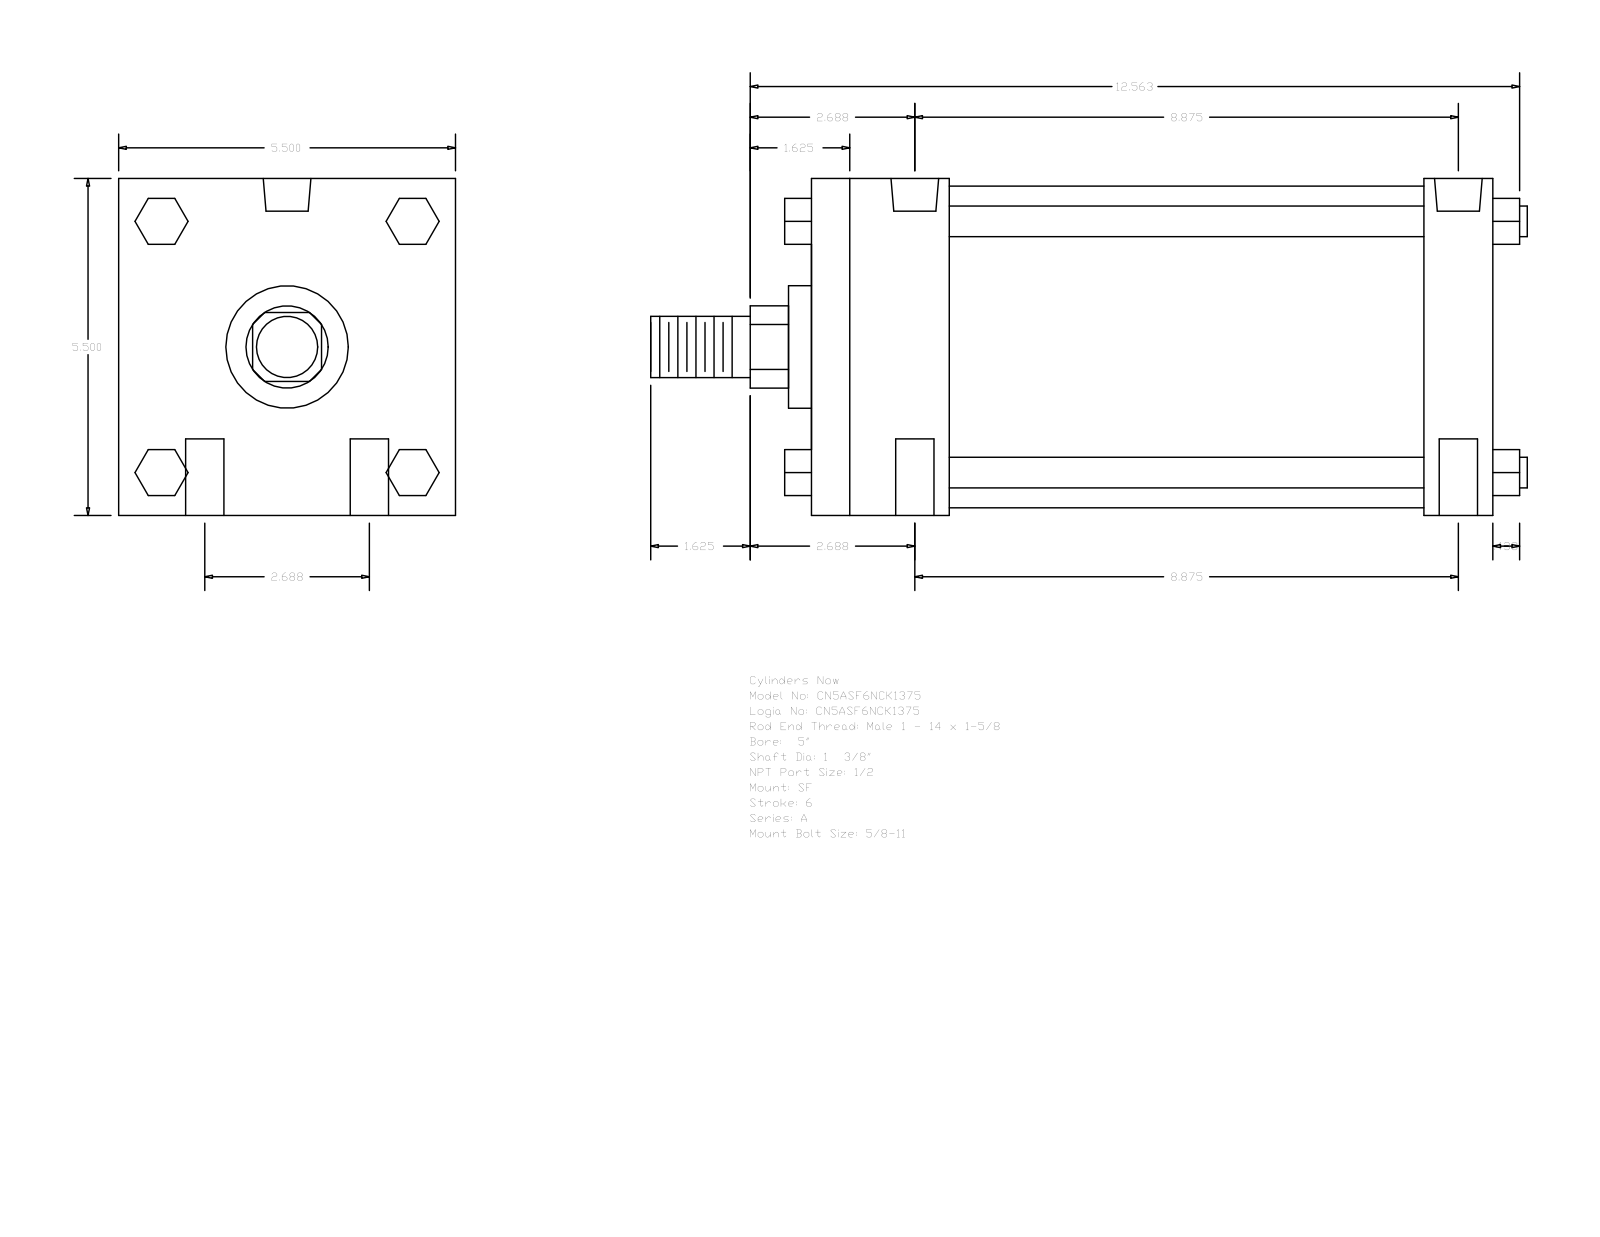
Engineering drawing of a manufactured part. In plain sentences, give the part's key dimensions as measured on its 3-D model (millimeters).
The part is named "A_SF__0500_1.375". Its 3-D file was written by "GSSL Pune (CONFIG_CONTROL_DESIGN)". It is 0 solids with 124 faces: 94 planar, 30 cylindrical and 0 other. Overall it measures 363.54 by 139.7 by 139.7 millimeters. Round holes: 4 of diameter 15.88, 2 of diameter 8.73, 2 of diameter 19.77. Round bosses or shafts: 4 of diameter 12.7, 1 of diameter 133.35, 1 of diameter 50.8, 1 of diameter 34.92, 1 of diameter 25.4. Partial cylindrical surfaces (rounded edges, fillets, slot ends): 1 of radius 17.06. The main face-to-face distances are 139.7, 282.58, 57.15, 28.58, 254, 196.85, 225.43, 19.05, 52.07, 90.18. The hole center spacings are 34.13, 228, 225.43, 68.26, 235.54, 220.65.
